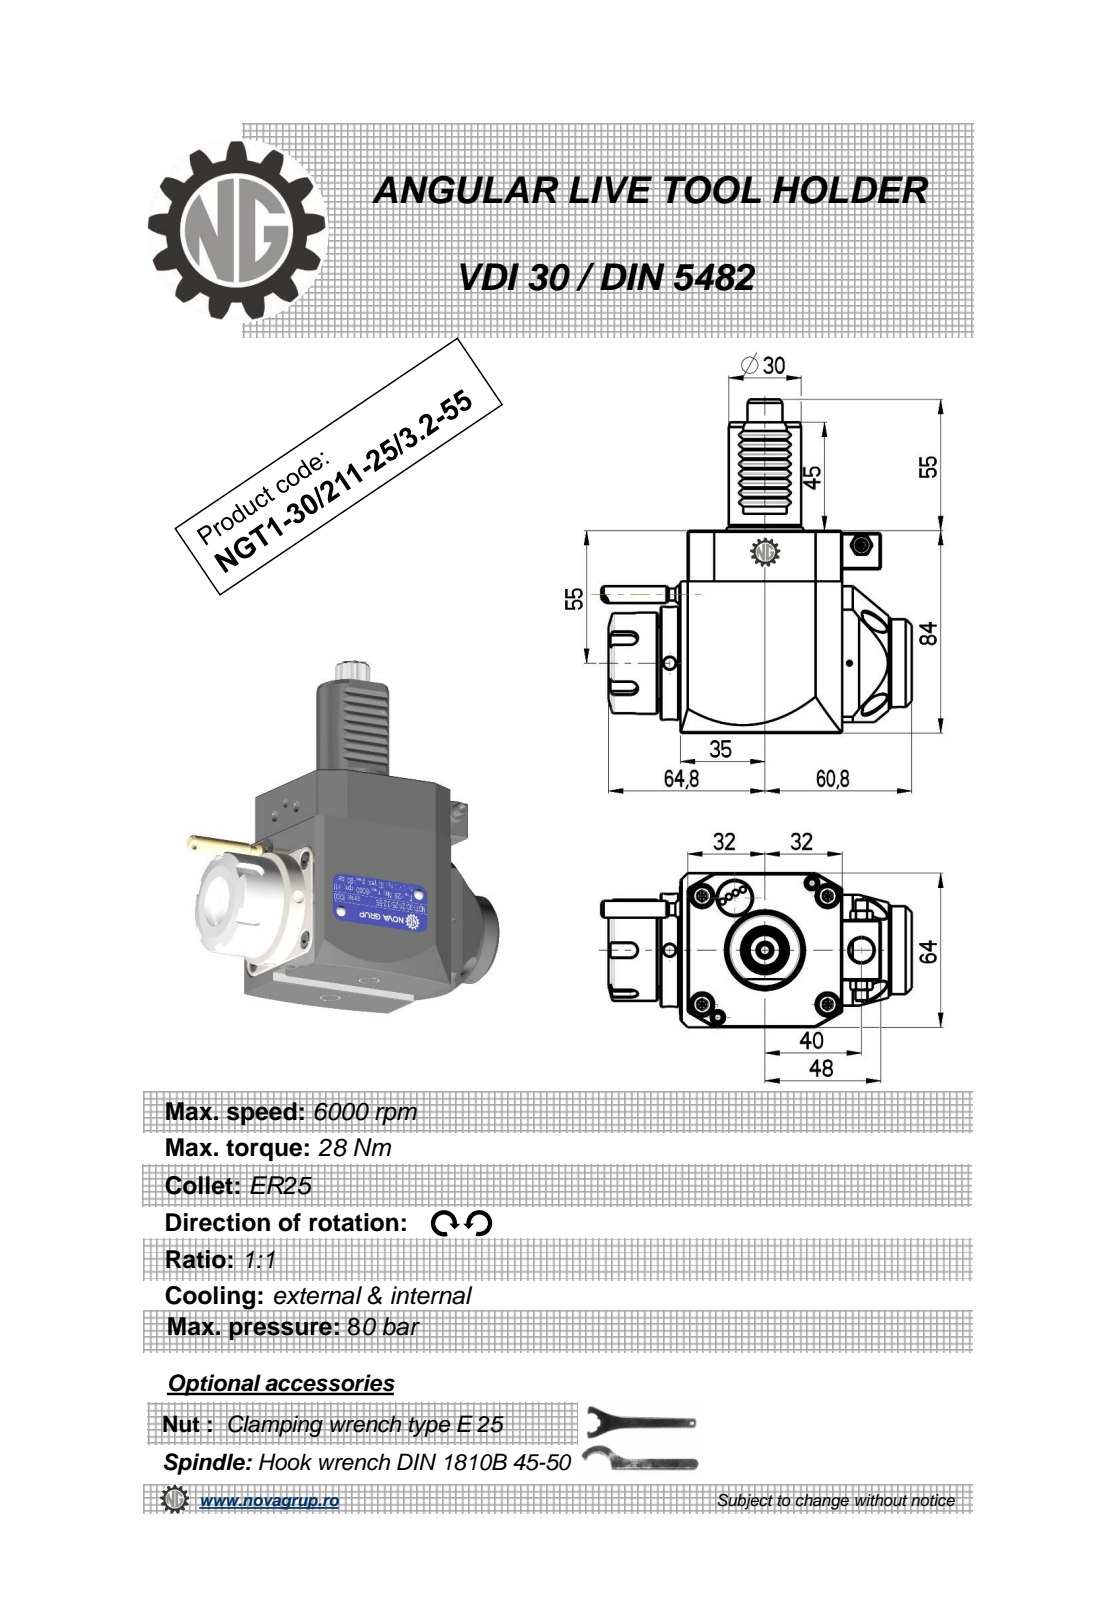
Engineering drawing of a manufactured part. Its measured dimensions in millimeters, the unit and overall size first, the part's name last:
Units: millimetres
Overall size (bounding box): 139 × 128.63 × 65.6
Round holes (diameter × count): ⌀5 ×2, ⌀2.5 ×1, ⌀3 ×1, ⌀4.2 ×1, ⌀9.5 ×1, ⌀10 ×1, ⌀20.3 ×1
Round bosses / shafts (diameter × count): ⌀8.96 ×2, ⌀5 ×2, ⌀47 ×1, ⌀42 ×1, ⌀36.5 ×1, ⌀35 ×1, ⌀30 ×1, ⌀7 ×1
Partial cylindrical surfaces — rounded edges, fillets, slot ends (radius × count): R2.91 ×16, R0.26 ×12, R0.3 ×8, R3 ×5, R160 ×2, R5.75 ×1, R7.25 ×1, R32 ×1
Main face-to-face distances: 64, 84, 0.5, 67.2, 67, 3.2, 3, 7.5, 80, 8
Hole centre spacings: 24.76, 33.19, 46.5, 79.45, 93.35
Volume: 469 732 mm³ · Surface area: 47 625 mm²
Bodies: 1 solid, 448 faces (176 planar, 110 cylindrical, 162 other)
Part name (STEP PRODUCT): NGT1_30_211_25_3_2_55
STEP written by: PRO/ENGINEER BY PARAMETRIC TECHNOLOGY CORPORATION, 2010280 (CONFIG_CONTROL_DESIGN)
